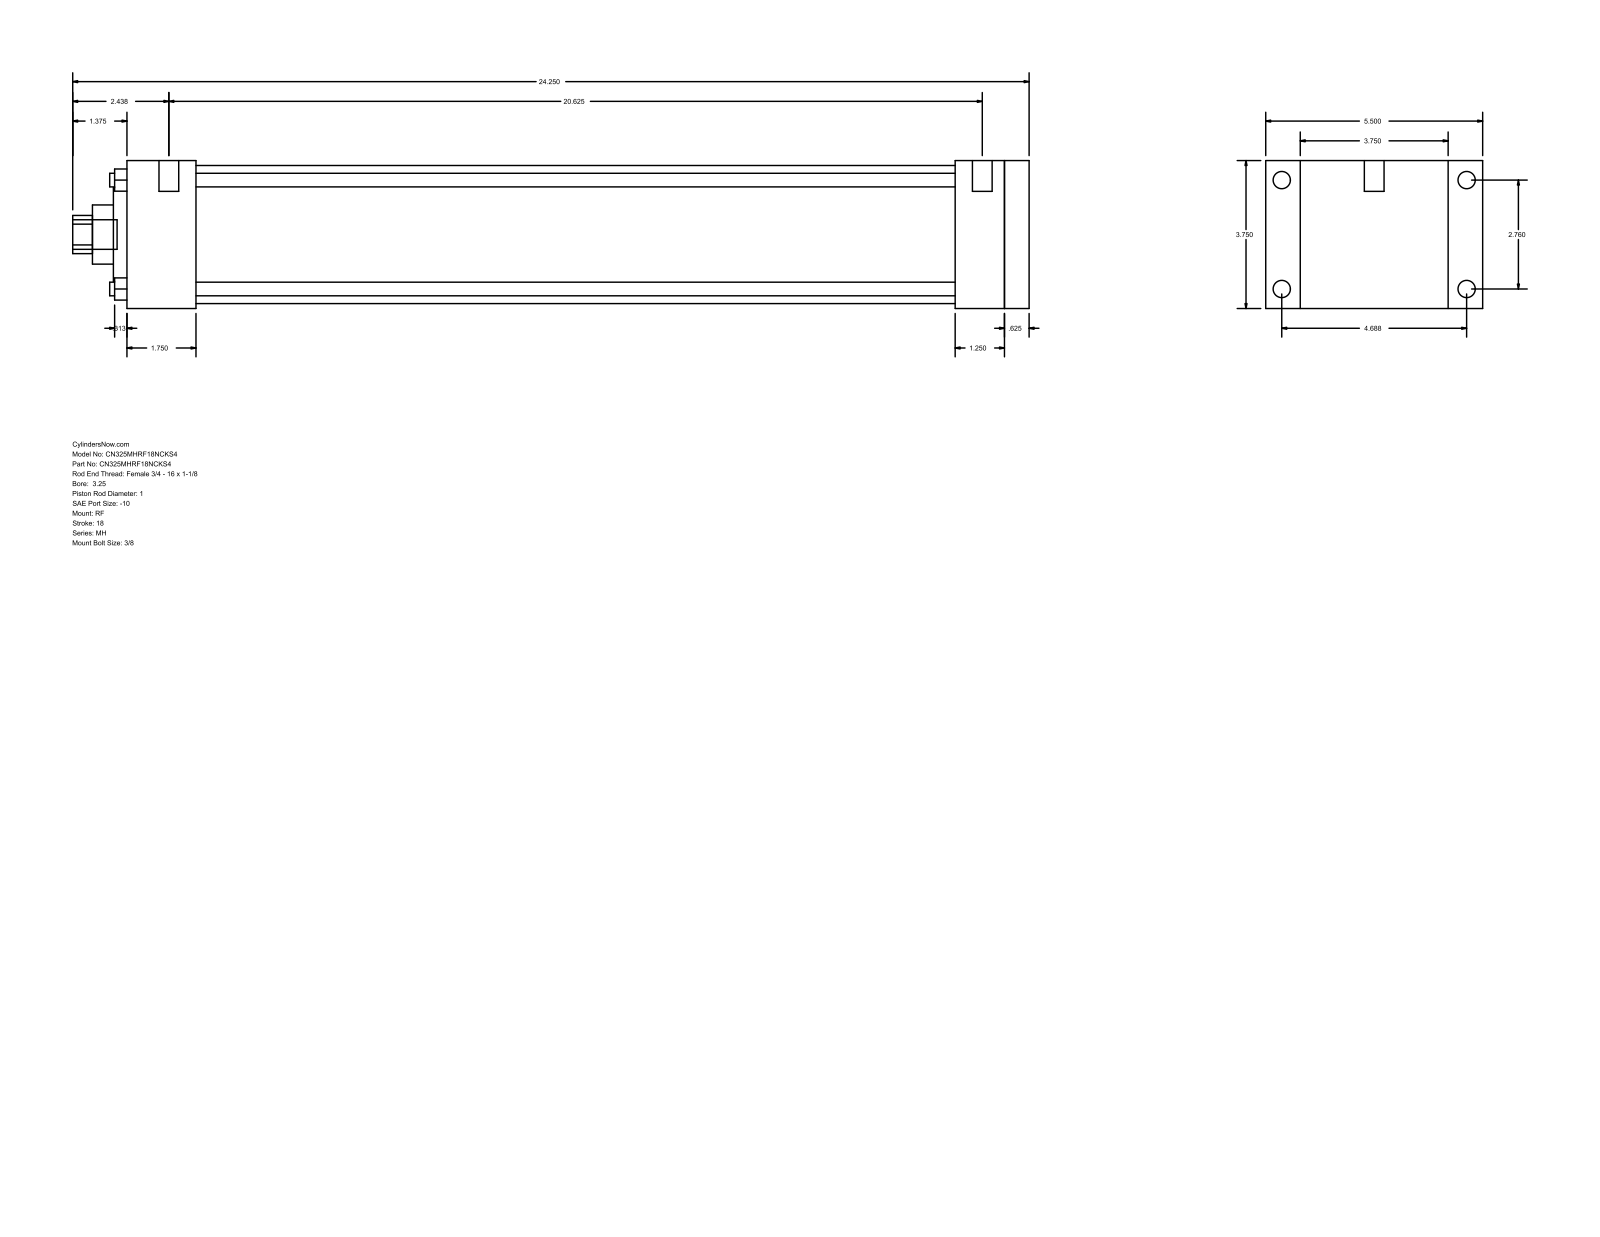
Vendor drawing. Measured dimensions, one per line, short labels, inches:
name: MH_RF__0325_1
written by: GSSL Pune (CONFIG_CONTROL_DESIGN)
unit: in
bodies: 0 solids, 94 faces (65 planar, 29 cylindrical, 0 other)
size: 24.25 × 5.5 × 3.75
holes: 4× ⌀0.345, 1× ⌀1, 1× ⌀1.5, 1× ⌀2.375, 1× ⌀3.5
bosses: 4× ⌀0.438, 4× ⌀0.219, 2× ⌀0.5, 1× ⌀0.75
rounds: 1× R0.484
face distances: 3.75, 22.875, 0.625, 22.25, 0.875, 4.625, 1.75, 20.5, 21.125, 21
hole spacings: 1.952, 2.76, 3.903
